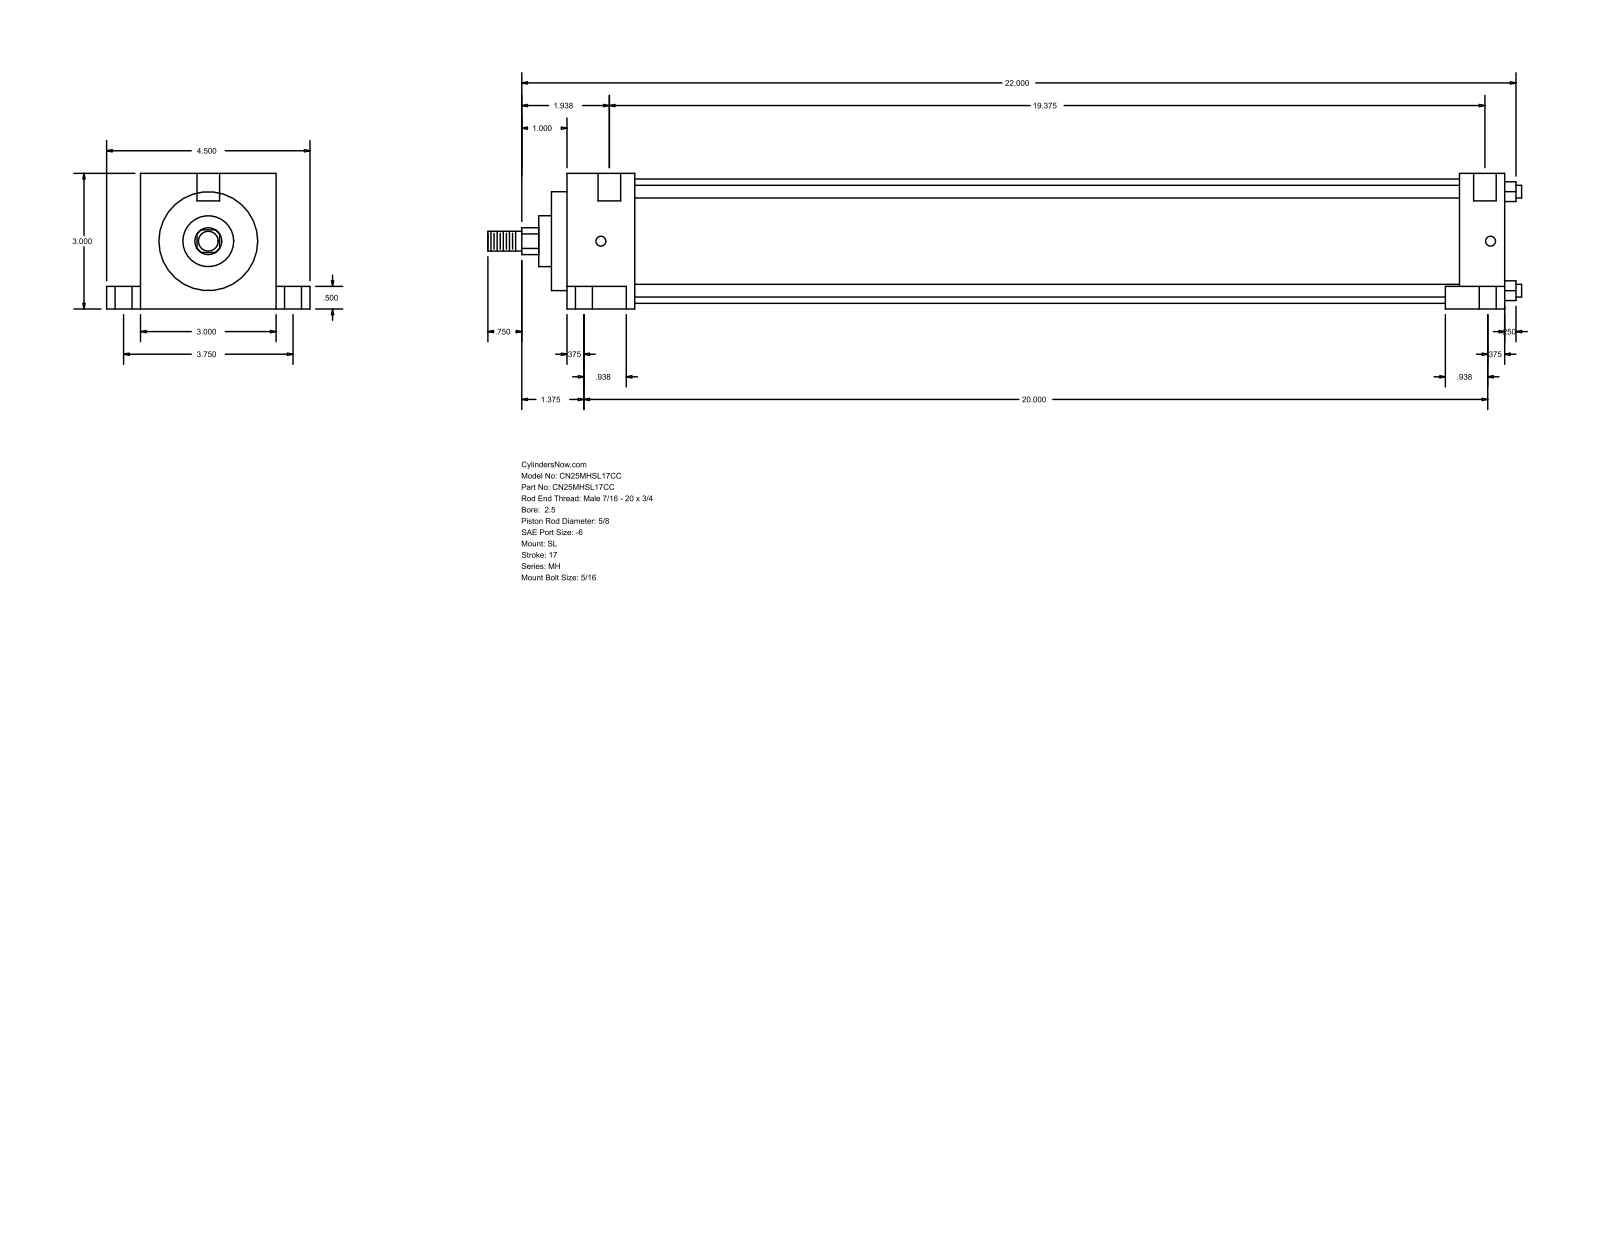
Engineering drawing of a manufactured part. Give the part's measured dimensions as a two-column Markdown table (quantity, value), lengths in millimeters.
| quantity | value |
| --- | --- |
| part name | MH_SL__0250_0.625 |
| STEP written by | GSSL Pune (CONFIG_CONTROL_DESIGN) |
| units | millimeters |
| bodies | 0 solids, 86 faces (61 planar, 25 cylindrical, 0 other) |
| overall size | 581.02 × 114.3 × 76.2 |
| round holes (diameter × count) | 5.56 × 2, 9.53 × 2, 15.88 × 2, 12.7 × 1 |
| round bosses / shafts (diameter × count) | 7.14 × 4, 69.85 × 1, 55.55 × 1, 28.57 × 1, 15.88 × 1, 11.11 × 1 |
| partial cylindrical surfaces (radius × count) | 7.54 × 1 |
| main face-to-face distances | 76.2, 25.4, 510.38, 535.78, 63.5, 12.7, 19.05, 95.25, 31.75, 502.44 |
| hole center spacings | 47.65, 3.17, 95.24 |
